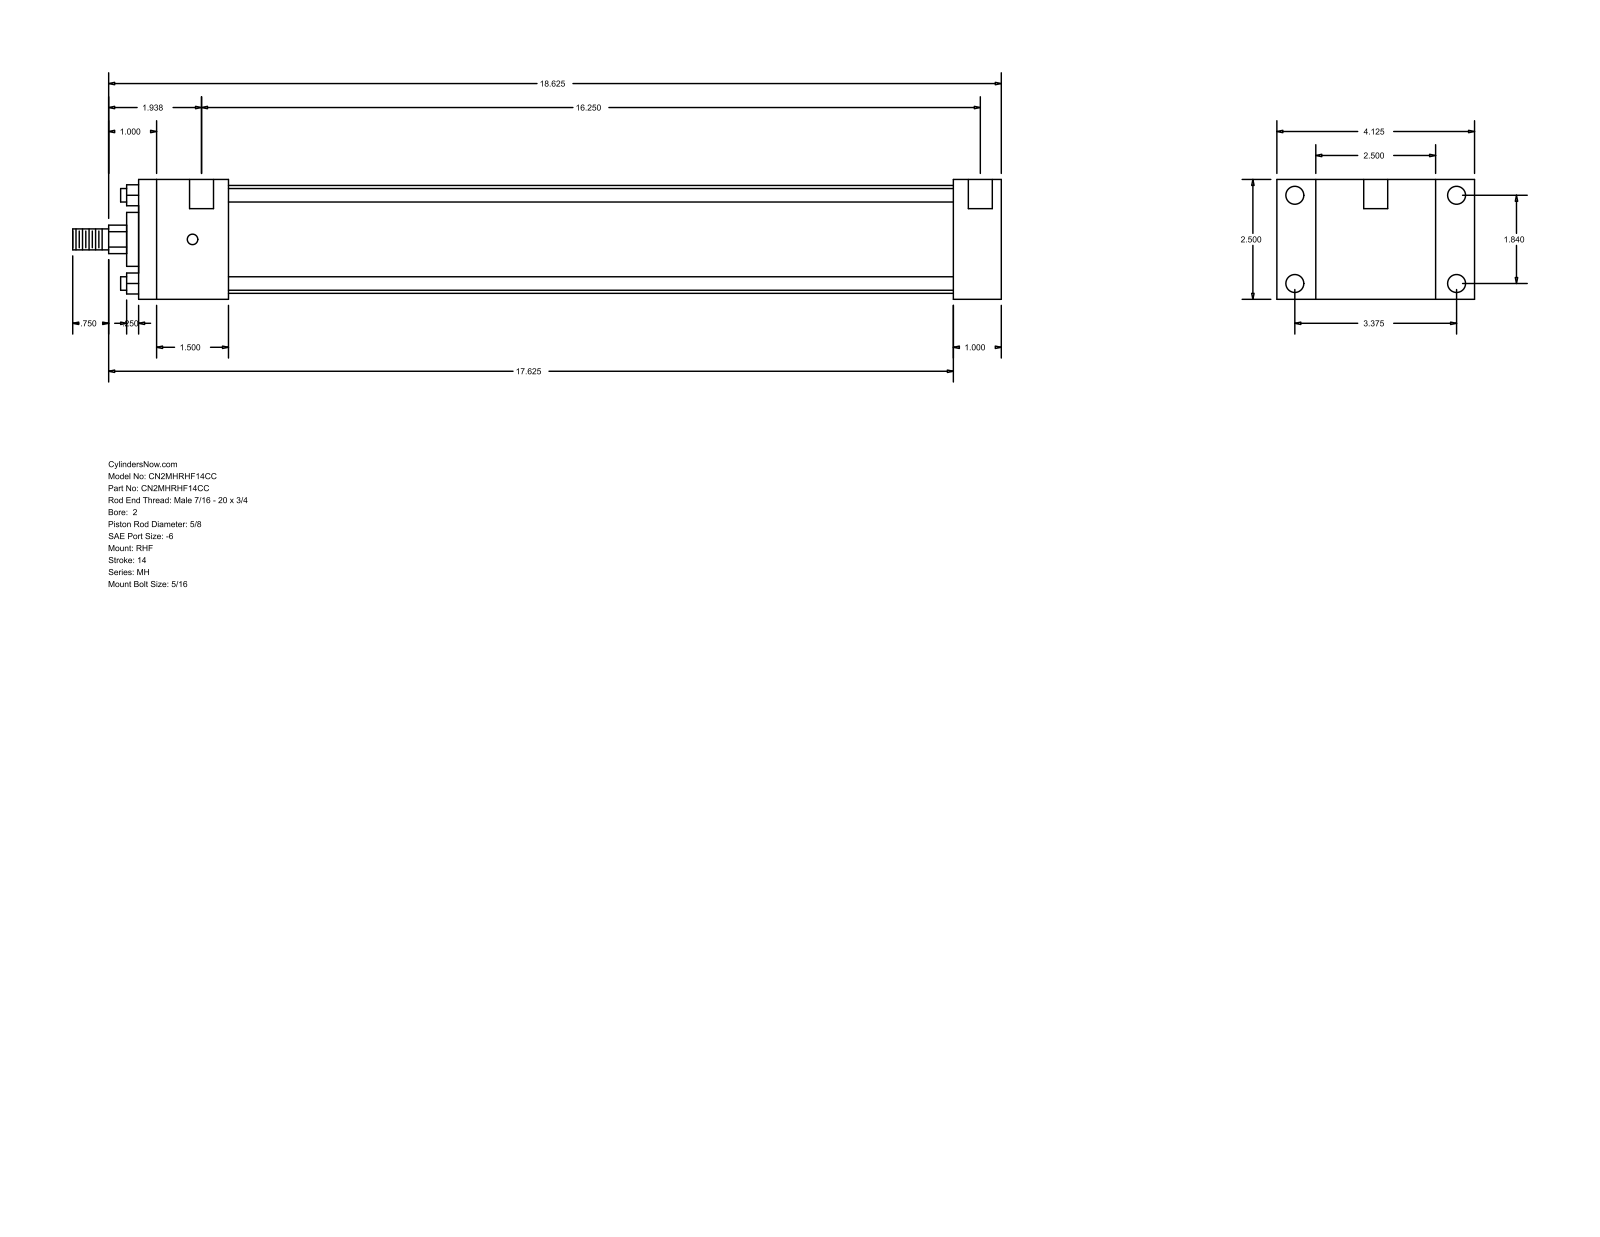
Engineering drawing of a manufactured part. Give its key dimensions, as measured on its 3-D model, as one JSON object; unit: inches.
{"part_name": "MH_RHF__0200_0.625", "step_written_by": "GSSL Pune (CONFIG_CONTROL_DESIGN)", "units": "inches", "bodies": {"solids": 0, "faces": 88, "planar": 60, "cylindrical": 28, "other": 0}, "overall_size": [19.375, 4.125, 2.5], "round_holes": [[0.219, 4], [0.375, 4], [0.5, 2]], "round_bosses_or_shafts": [[0.281, 4], [2.25, 1], [1.125, 1], [0.625, 1], [0.437, 1]], "partial_cylinders_radius": [[0.297, 1]], "face_to_face_distances": [2.5, 1, 0.813, 3.313, 17, 18, 4.125, 1.875, 15.125, 16.125], "hole_center_spacings": [1.84, 3.375, 3.844, 16.563, 0.125, 0.187, 16.25, 16.375]}
